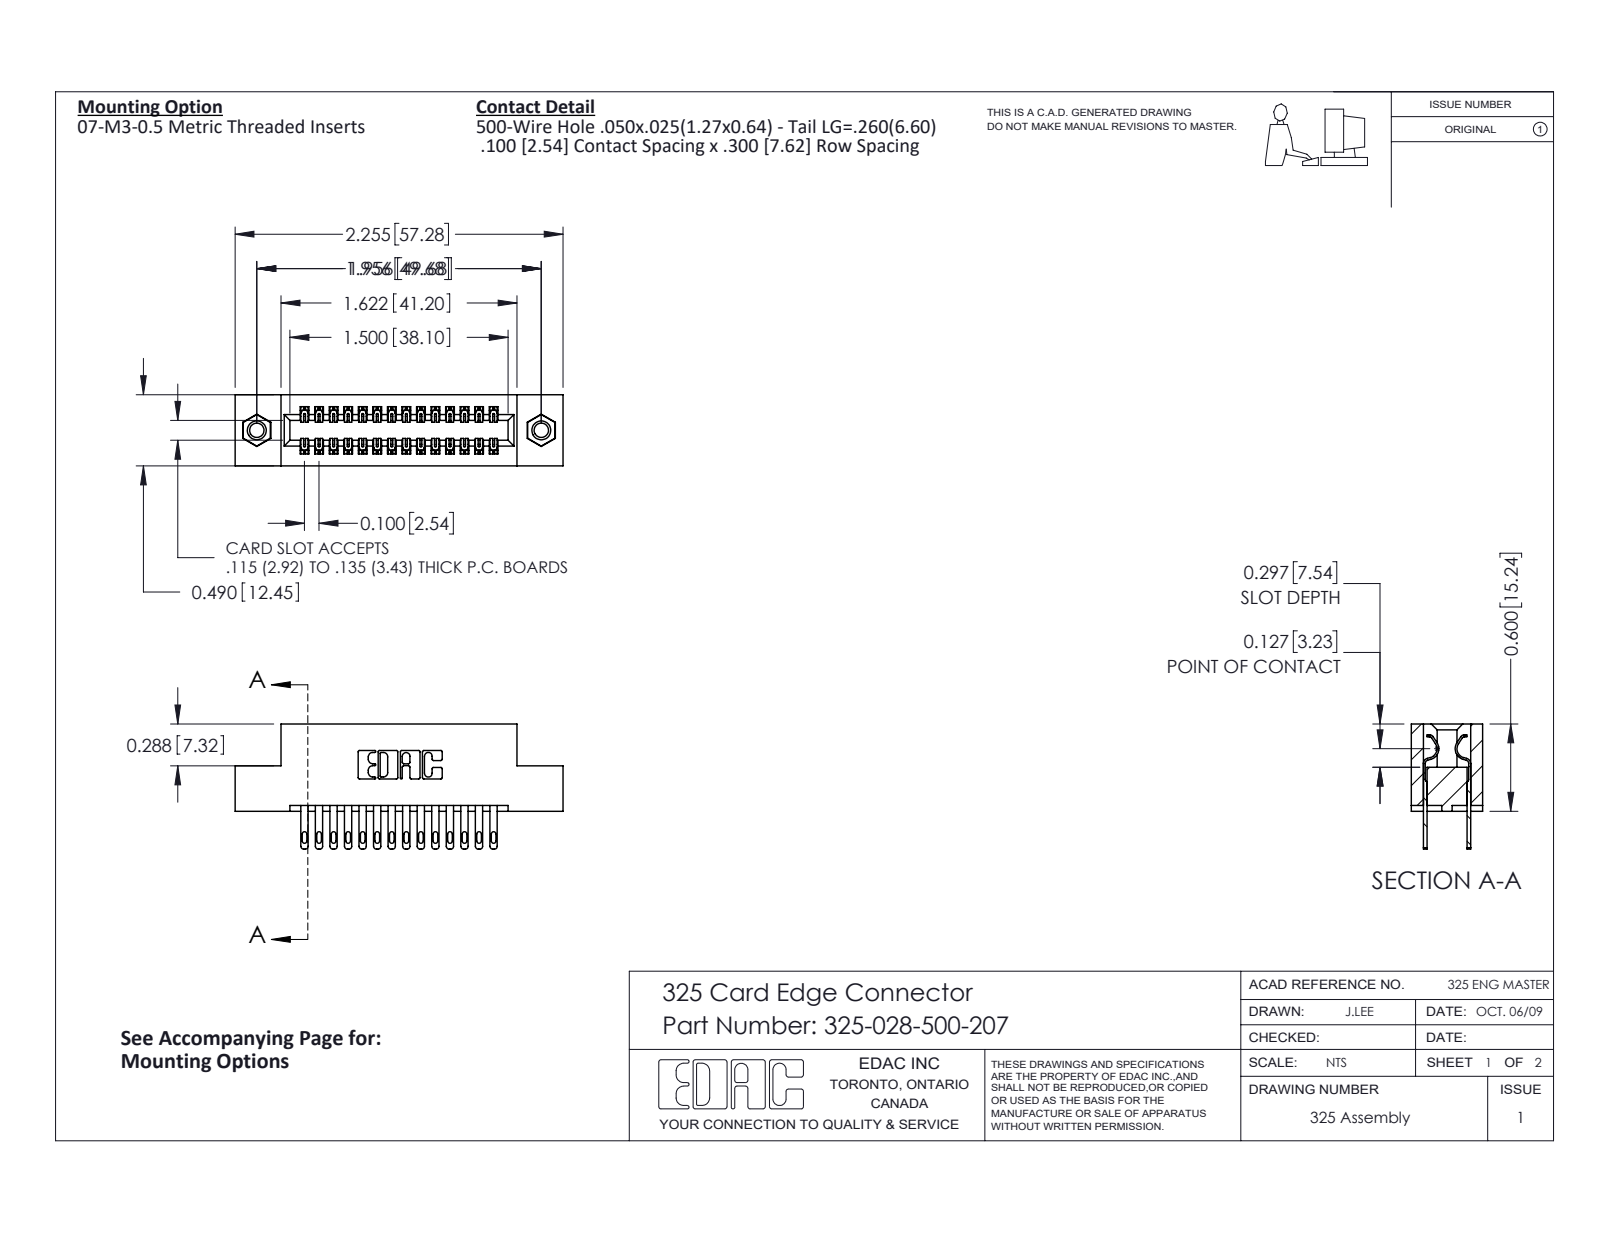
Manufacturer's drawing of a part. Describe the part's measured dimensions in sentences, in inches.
The part is named "345-250-001_345-250-005-103; 325-292-001_325-293-100; 325-028-500-207; 325 Part_TI". Its 3-D file was written by "SolidWorks 2016 (CONFIG_CONTROL_DESIGN)". It is 31 solids with 1518 faces: 942 planar, 560 cylindrical and 16 other. Overall it measures 2.255 by 0.86 by 0.49 inches. Its volume is 0.44 cubic inches and its surface area 13 square inches. Round holes: 2 of diameter 0.098, 2 of diameter 0.125, 2 of diameter 0.16. Round bosses or shafts: 2 of diameter 0.155. Partial cylindrical surfaces (rounded edges, fillets, slot ends): 42 of radius 0.006, 28 of radius 0.016, 28 of radius 0.02, 22 of radius 0.01, 6 of radius 0.007, 6 of radius 0.031, 3 of radius 0.026, 2 of radius 0.014. The main face-to-face distances are 0.083, 0.407, 0.3, 0.49, 0.107, 0.383, 0.025, 0.325, 0.04, 0.1. The hole center spacings are 1.956.
